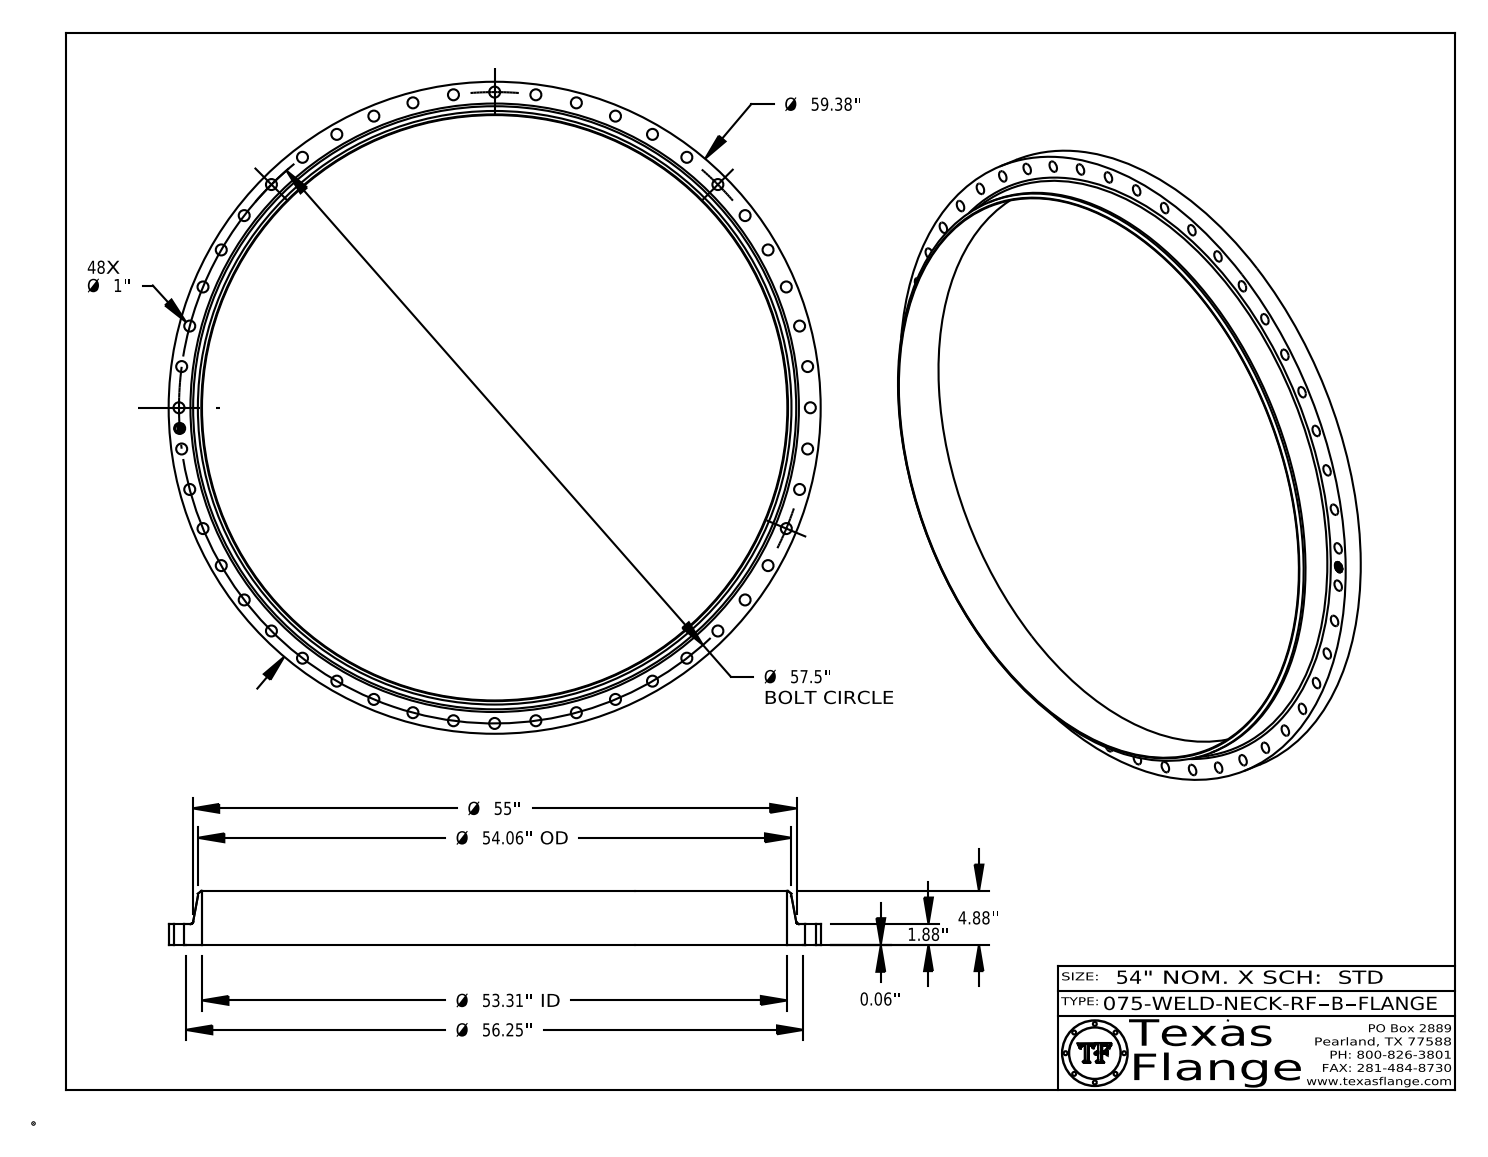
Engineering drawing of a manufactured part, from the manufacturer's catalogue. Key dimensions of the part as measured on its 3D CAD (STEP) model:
Part name (STEP PRODUCT): 075-WELD-NECK-RF, Series B
STEP written by: CATIA V5 STEP AP214 (AUTOMOTIVE_DESIGN)
Units: inches
Bodies: 1 solid, 499 faces (369 planar, 124 cylindrical, 6 other)
Overall size (bounding box): 59.38 × 59.38 × 4.943
Volume: 1 241 in³ · Surface area: 2 874 in²
Round holes (diameter × count): ⌀1 ×49, ⌀53.31 ×1
Round bosses / shafts (diameter × count): ⌀0.061 ×8, ⌀59.38 ×1, ⌀56.25 ×1, ⌀54.06 ×1, ⌀0.788 ×1
Main face-to-face distances: 1.943, 0.063, 1.88, 4.943, 4.88, 3, 0.015, 1.928, 1.865, 3.015
Hole centre spacings: 28.75, 11.218, 57.377, 3.761, 22.004, 57.008, 7.505, 14.882
